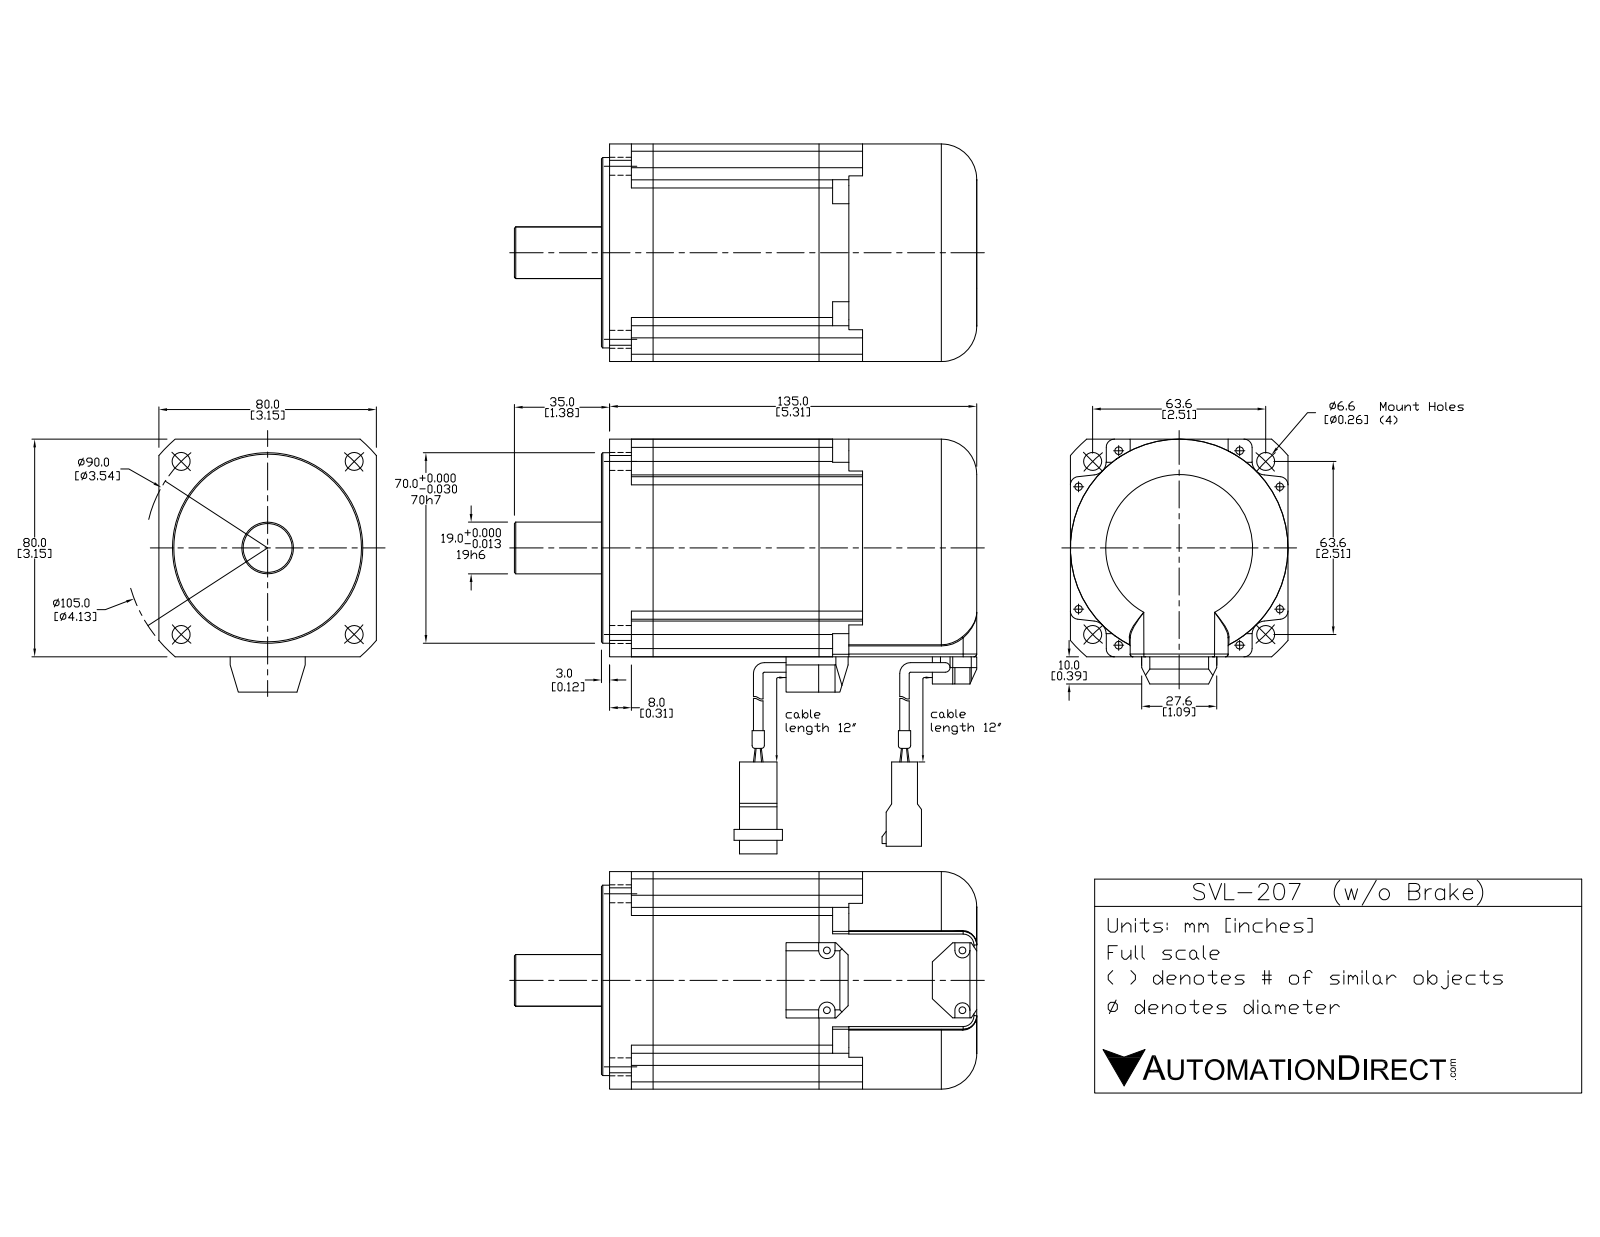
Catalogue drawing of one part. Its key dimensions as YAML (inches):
part_name: "SVL-207"
step_written_by: "SolidWorks 2015 (AUTOMOTIVE_DESIGN)"
units: inches
bodies: {solids: 18, faces: 415, planar: 265, cylindrical: 113, other: 37}
overall_size: [6.772, 3.677, 3.15]
volume: 47.39
surface_area: 146.3
round_holes:
  - {diameter: 0.26, count: 4}
  - {diameter: 0.866, count: 1}
round_bosses_or_shafts:
  - {diameter: 0.197, count: 8}
  - {diameter: 0.276, count: 5}
  - {diameter: 3.15, count: 1}
  - {diameter: 2.756, count: 1}
  - {diameter: 0.748, count: 1}
  - {diameter: 0.217, count: 1}
partial_cylinders:
  - {radius: 0.039, count: 14}
  - {radius: 0.118, count: 12}
  - {radius: 0.079, count: 4}
  - {radius: 0.108, count: 4}
  - {radius: 0.197, count: 4}
  - {radius: 2.067, count: 1}
face_to_face_distances: [3.15, 2.402, 2.835, 0.433, 2.283, 1.85, 4.685, 0.52, 2.63, 0.748]
hole_center_spacings: [1.772, 2.506, 3.543]
